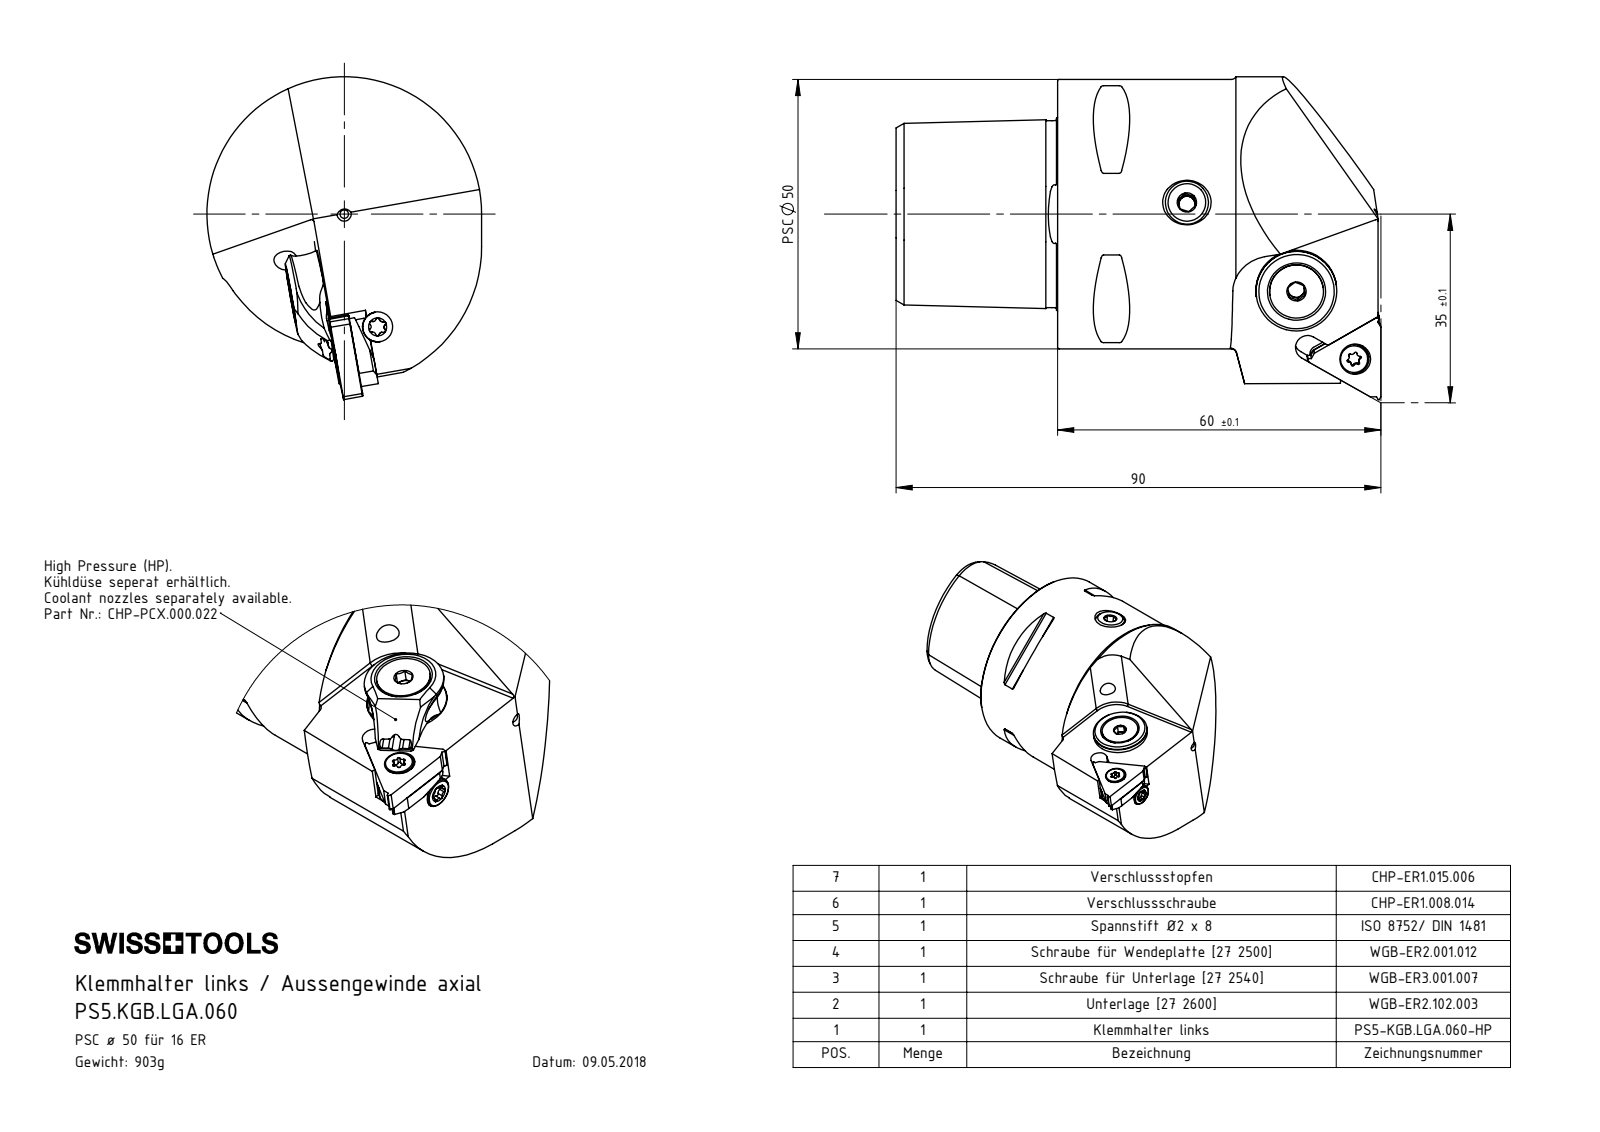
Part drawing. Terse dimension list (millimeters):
name: KVT_MB_600_050; PS5-KGB.LGA.060_A_Fertigbearbeitung; WGB-ER2.102.003_A alt; WGB-ER3.001.007_A (+3 more)
written by: SolidWorks 2022 (AUTOMOTIVE_DESIGN)
unit: mm
bodies: 7 solids, 322 faces (88 planar, 100 cylindrical, 134 other)
size: 90 × 59.91 × 50.5
volume: 104 933 mm³; area: 20 782 mm²
holes: 3× ⌀4, 2× ⌀2.58, 2× ⌀4.2, 1× ⌀4.02, 1× ⌀6.1, 1× ⌀14.5, 1× ⌀21, 1× ⌀24
bosses: 2× ⌀5.5, 1× ⌀50, 1× ⌀5, 1× ⌀3.18, 1× ⌀3, 1× ⌀2.78
rounds: 8× R0.5, 6× R0.23, 6× R0.34, 6× R0.57, 6× R0.57, 2× R0.1, 1× R0.25, 1× R1.3
face distances: 30, 19.18, 3.45, 3.2, 6.65, 44.4, 6.85, 3.65, 20, 10
hole spacings: 26, 467.55, 467.6
